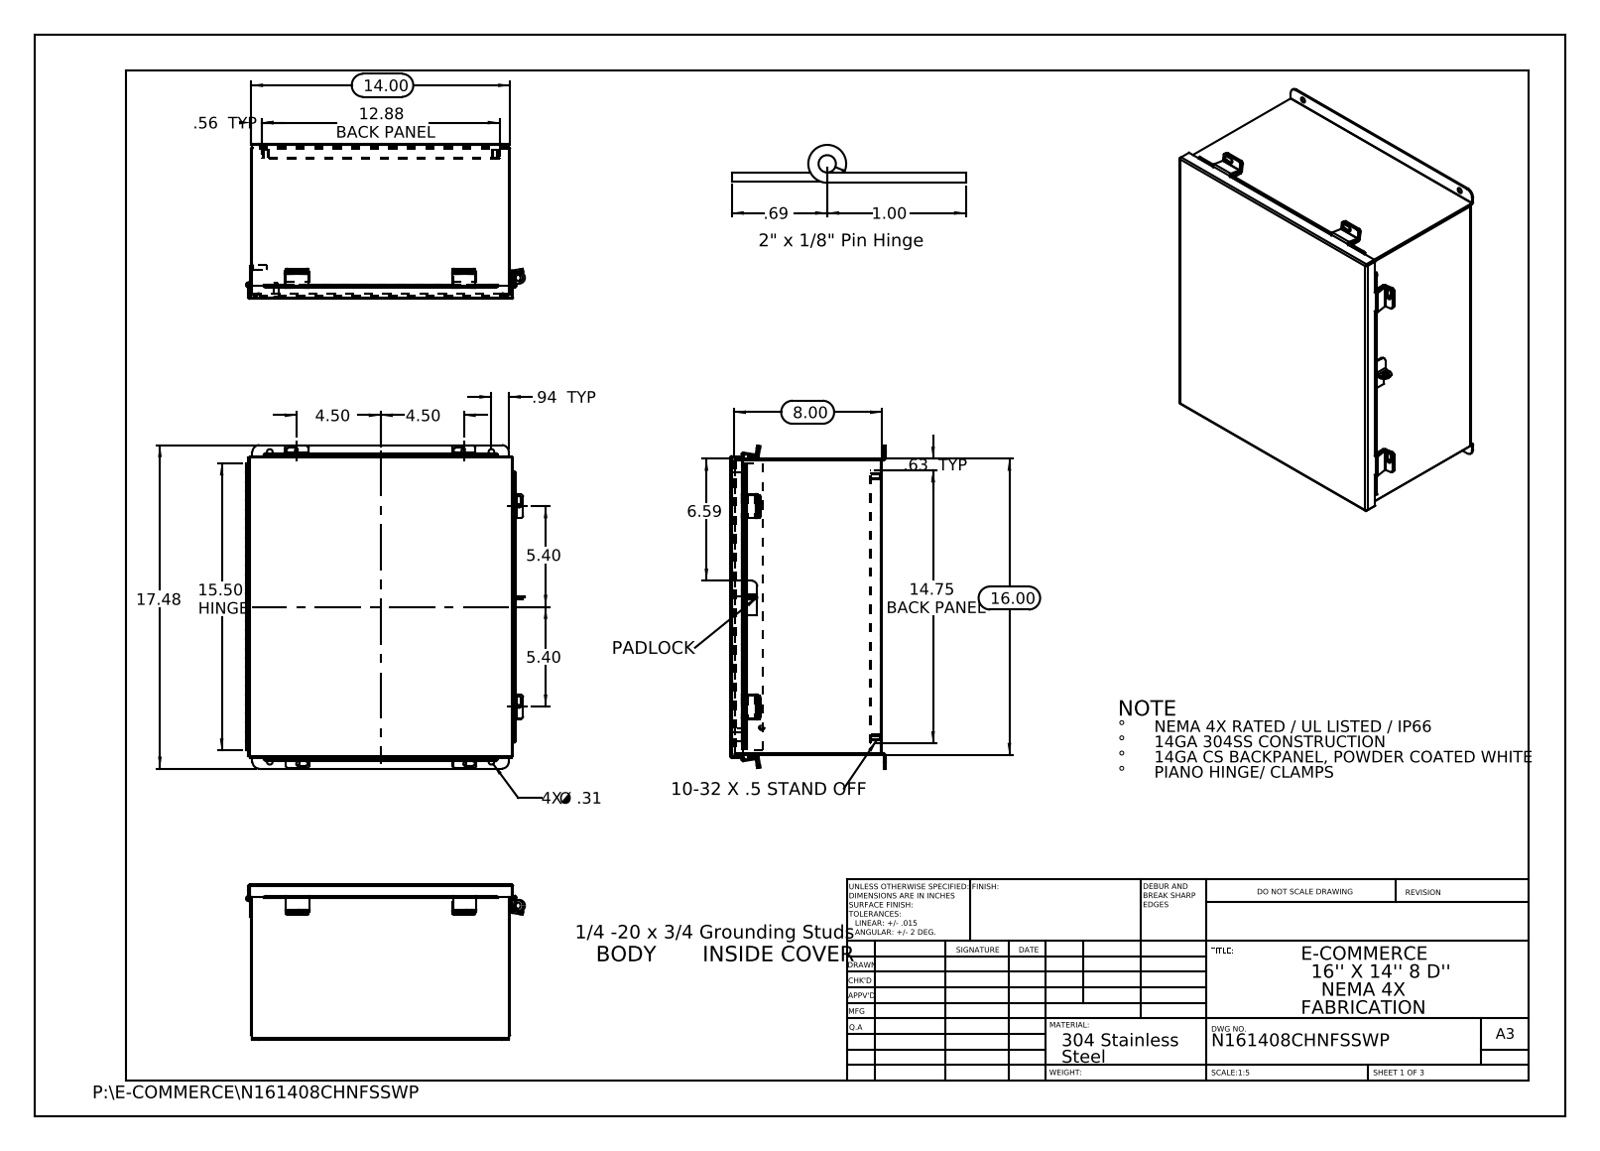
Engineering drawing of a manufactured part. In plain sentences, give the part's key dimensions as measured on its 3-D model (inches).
The part is named "N161408CHNFSSWP HW-CD-S-25020-034; N161408CHNFSSWP JIC Clamp Bracket; N161408CHNFSSWP JIC_Cover_Template; N161408CHNFSSWP JIC Backpanel (+8 more)". Its 3-D file was written by "SolidWorks 2013 (CONFIG_CONTROL_DESIGN)". It is 27 solids with 866 faces: 539 planar, 307 cylindrical and 20 other. Overall it measures 17.476 by 15.072 by 8.39 inches. Its volume is 93.71 cubic inches and its surface area 2 546 square inches. Round holes: 10 of diameter 0.25, 4 of diameter 0.187, 4 of diameter 0.312, 1 of diameter 0.125, 1 of diameter 0.125, 1 of diameter 0.373, 1 of diameter 0.375. Round bosses or shafts: 4 of diameter 0.313, 2 of diameter 0.315, 2 of diameter 0.236, 1 of diameter 0.273, 1 of diameter 0.25. Partial cylindrical surfaces (rounded edges, fillets, slot ends): 23 of radius 0.125, 13 of radius 0.013, 12 of radius 0.009, 12 of radius 0.088, 12 of radius 0.133, 6 of radius 0.083, 6 of radius 0.1, 4 of radius 0.375. The main face-to-face distances are 0.075, 8.128, 13.925, 15.925, 8.053, 8.203, 7.628, 0.575, 0.5, 7.553. The hole center spacings are 1.315, 12.244, 15.427, 19.652, 9, 11.976, 12.375, 14.126.
